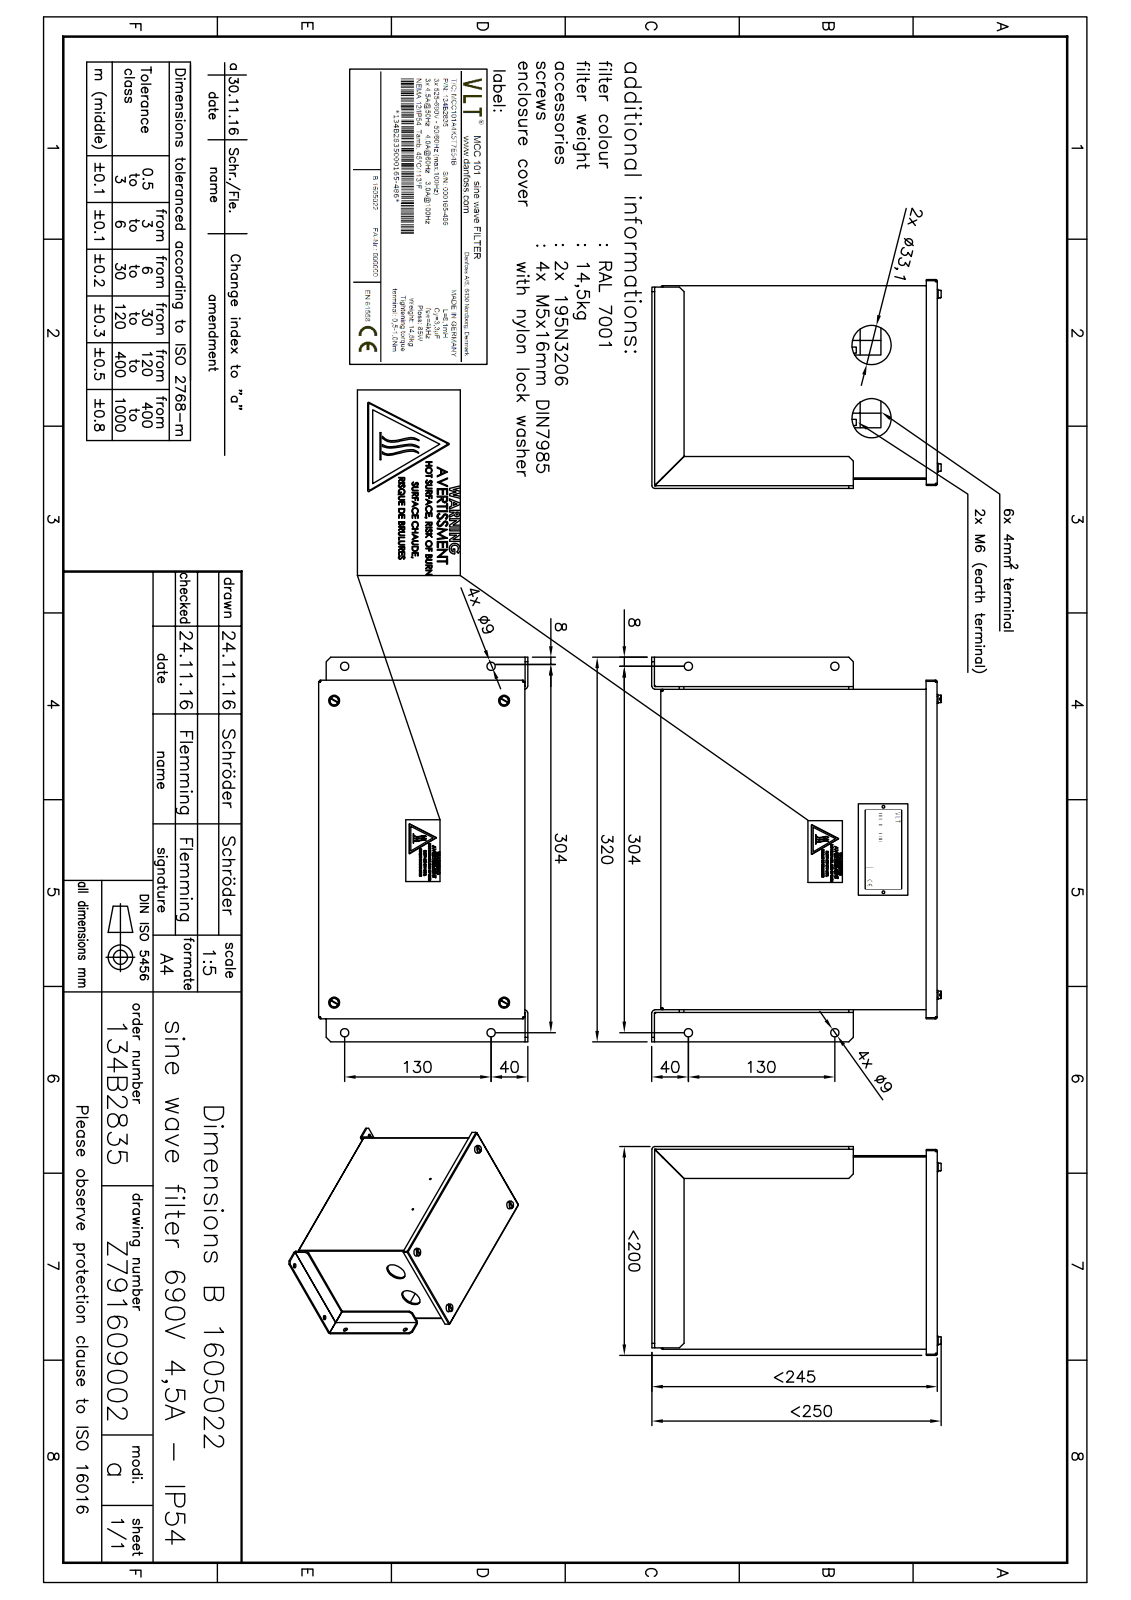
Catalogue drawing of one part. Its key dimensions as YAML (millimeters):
part_name: "pan head cross recess screw_din; WickelUI90_51,5_1oD; plain washer grade a_din_Washer DIN 125 - A 5.3; Deckel #020-2946 (+8 more)"
step_written_by: "SolidWorks 2014 (AUTOMOTIVE_DESIGN)"
units: millimeters
bodies: {solids: 40, faces: 2211, planar: 1117, cylindrical: 758, other: 336}
overall_size: [320, 245.63, 198.93]
volume: 2326000
surface_area: 1282000
round_holes:
  - {diameter: 5.5, count: 9}
  - {diameter: 3.7, count: 8}
  - {diameter: 9, count: 8}
  - {diameter: 6, count: 7}
  - {diameter: 8.5, count: 6}
  - {diameter: 5, count: 5}
  - {diameter: 4.5, count: 4}
  - {diameter: 5.3, count: 4}
  - {diameter: 6.2, count: 4}
  - {diameter: 3.3, count: 2}
  - {diameter: 7.15, count: 2}
  - {diameter: 7.8, count: 2}
round_bosses_or_shafts:
  - {diameter: 10, count: 4}
  - {diameter: 9.5, count: 4}
  - {diameter: 5, count: 4}
  - {diameter: 8.5, count: 2}
  - {diameter: 8, count: 2}
  - {diameter: 6.95, count: 2}
partial_cylinders:
  - {radius: 0.5, count: 76}
  - {radius: 2, count: 66}
  - {radius: 0.2, count: 28}
  - {radius: 0.1, count: 25}
  - {radius: 1.1, count: 18}
  - {radius: 6, count: 12}
  - {radius: 10, count: 12}
  - {radius: 1, count: 8}
face_to_face_distances: [1, 1.5, 279, 179, 230, 180, 60, 180.5, 181.5, 231]
hole_center_spacings: [60, 120, 6.73, 41.8, 130, 134.16, 304, 330.63]
